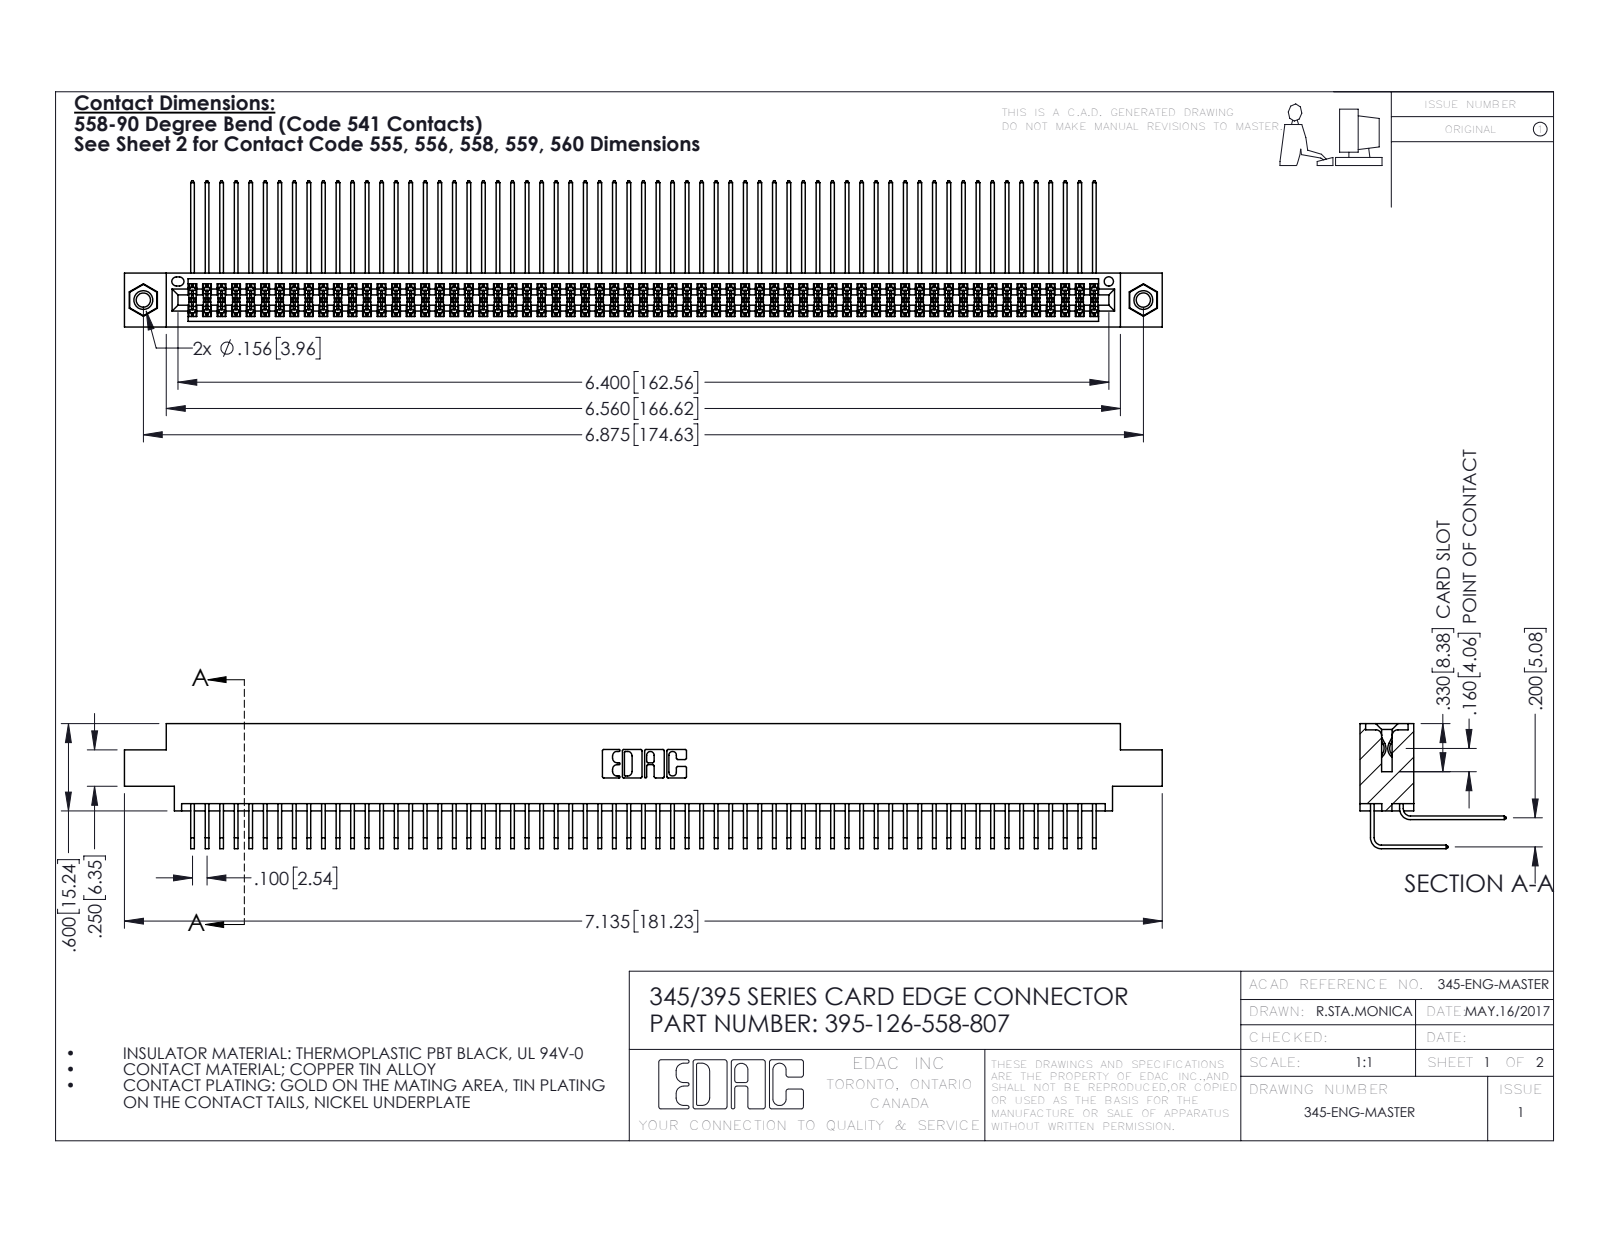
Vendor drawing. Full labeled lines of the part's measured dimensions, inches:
Part name (STEP PRODUCT): 345-292-001_558 559 Tail - 1; 345-250-001_345-250-005-103; 345 Part_0.170 Offset - 0.156 Dia-TI; 345-292-001_558 Tail - 2 (+1 more)
STEP written by: SolidWorks 2016 (CONFIG_CONTROL_DESIGN)
Units: inches
Bodies: 129 solids, 6742 faces (4526 planar, 2200 cylindrical, 16 other)
Overall size (bounding box): 7.135 × 1.005 × 0.859
Volume: 1.123 in³ · Surface area: 48.35 in²
Round holes (diameter × count): ⌀0.098 ×2, ⌀0.125 ×2, ⌀0.156 ×2, ⌀0.064 ×1
Round bosses / shafts (diameter × count): ⌀0.155 ×2
Partial cylindrical surfaces — rounded edges, fillets, slot ends (radius × count): R0.006 ×190, R0.01 ×22, R0.007 ×6, R0.031 ×6, R0.026 ×3, R0.014 ×2, R0.019 ×2, R0.022 ×2
Main face-to-face distances: 0.072, 0.298, 0.2, 0.37, 0.098, 0.272, 0.025, 0.225, 0.175, 0.025
Hole centre spacings: 0.27, 6.639, 6.875
